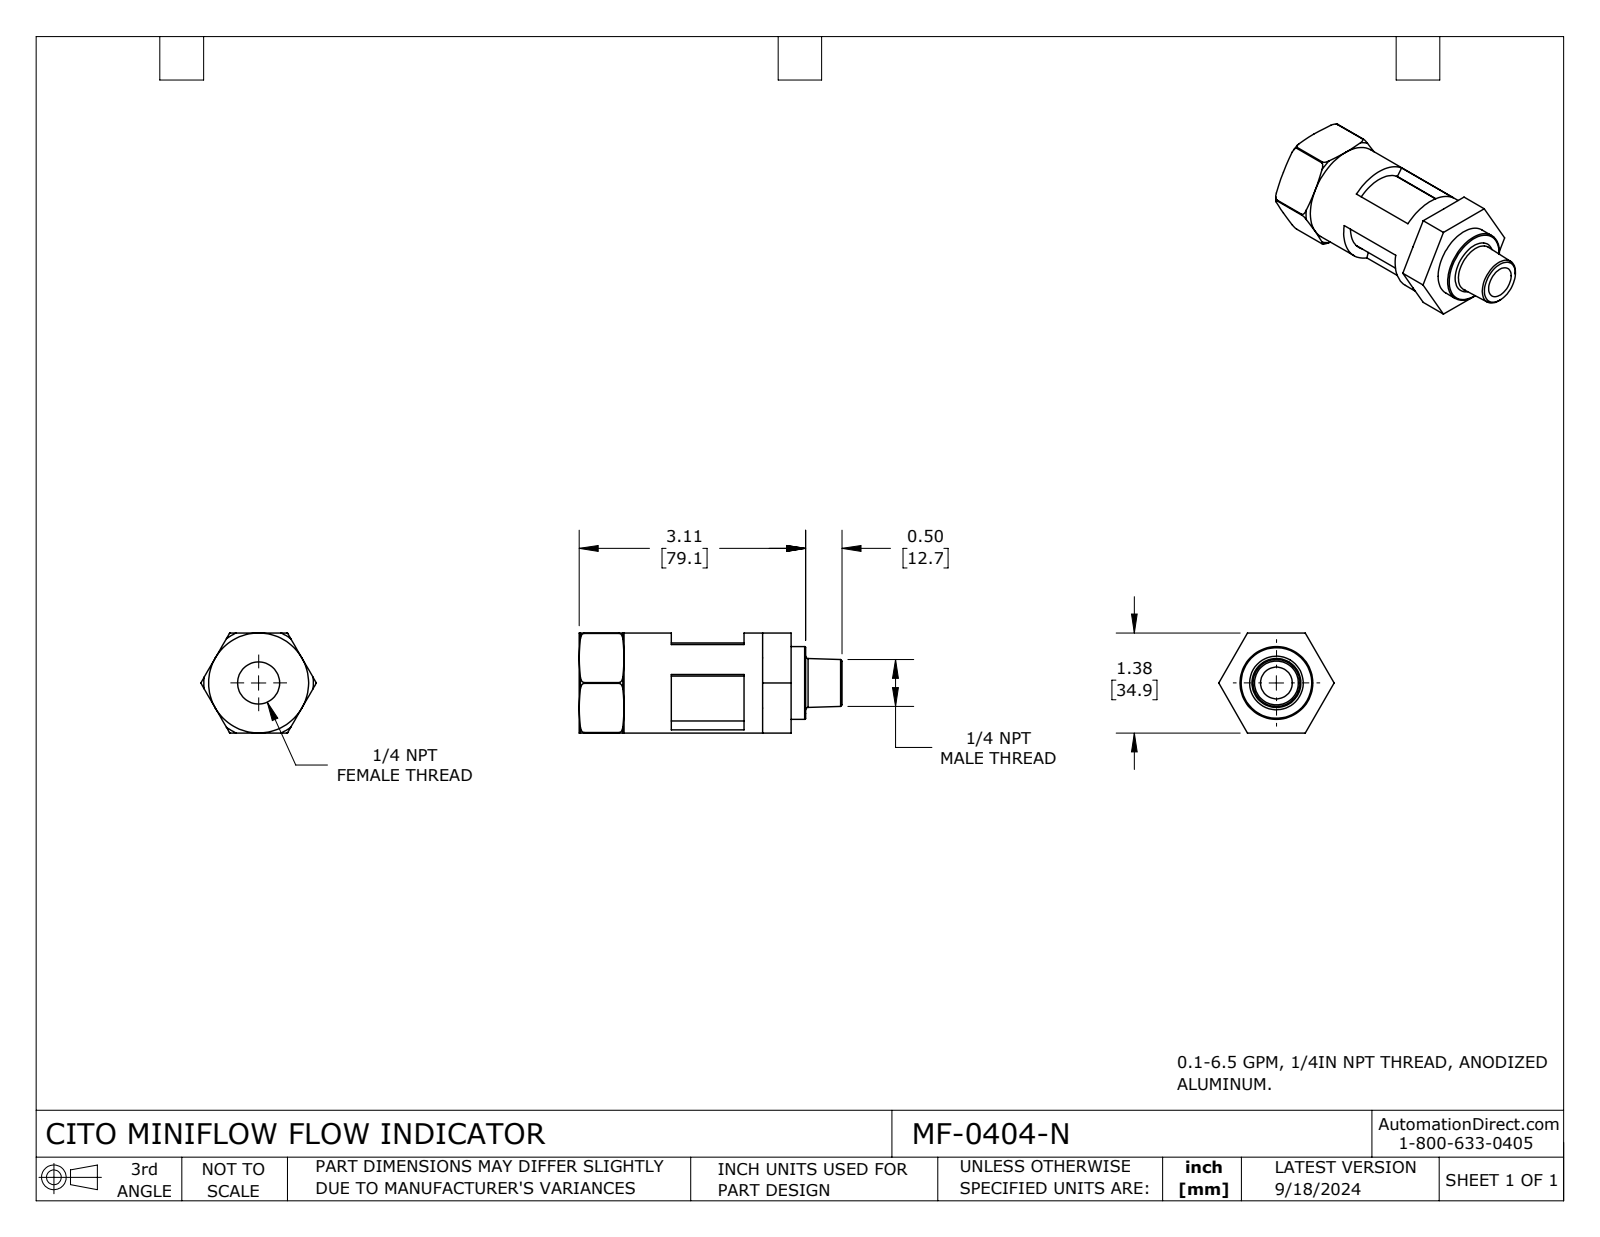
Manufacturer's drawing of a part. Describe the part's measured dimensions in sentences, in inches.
The part is named "MF-0404-N". Its 3-D file was written by "SolidWorks 2023 (CONFIG_CONTROL_DESIGN)". It is 2 solids with 97 faces: 40 planar, 23 cylindrical and 34 other. Overall it measures 3.615 by 1.588 by 1.375 inches. Its volume is 2.793 cubic inches and its surface area 34.41 square inches. Round holes: 1 of diameter 0.437, 1 of diameter 0.578, 1 of diameter 0.882, 1 of diameter 1.112. Round bosses or shafts: 1 of diameter 1.375, 1 of diameter 1.102, 1 of diameter 1. Partial cylindrical surfaces (rounded edges, fillets, slot ends): 1 of radius 0.79. The main face-to-face distances are 1.375, 2.521, 0.394, 2.915, 2.298, 1.904, 0.617, 0.457, 1.841, 3.115.
